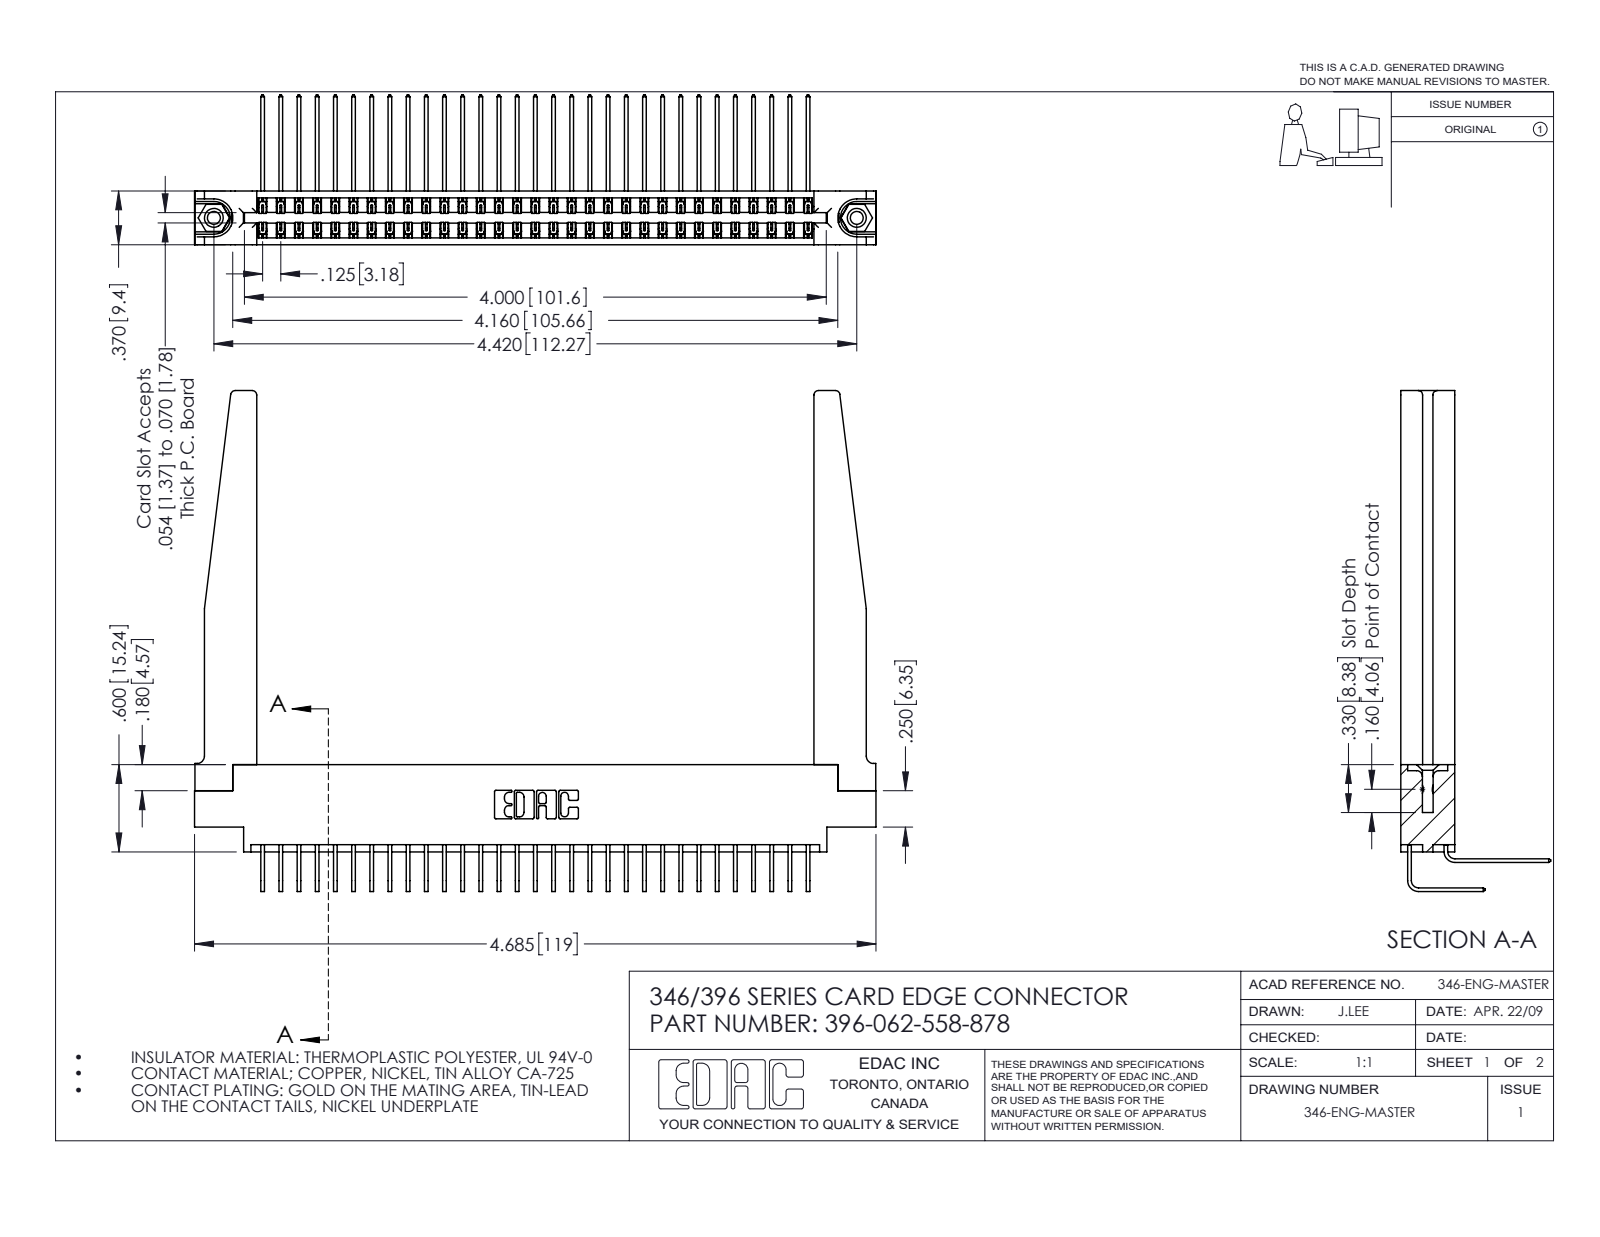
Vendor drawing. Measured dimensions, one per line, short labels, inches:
name: 346-220-078_345-220-078; 396-062-558-878; 346 Part_0.170 Offset - 0.156 Dia-TH; 345-292-001_558 Tail - 2 (+2 more)
written by: SolidWorks 2016 (CONFIG_CONTROL_DESIGN)
unit: in
bodies: 67 solids, 3708 faces (2516 planar, 1140 cylindrical, 52 other)
size: 4.685 × 3.443 × 1.03
volume: 1.137 in³; area: 37.78 in²
holes: 2× ⌀0.089, 2× ⌀0.125, 2× ⌀0.156, 1× ⌀0.064
bosses: 2× ⌀0.155
rounds: 93× R0.006, 22× R0.01, 8× R0.03, 6× R0.007, 6× R0.031, 4× R0.05, 3× R0.026, 2× R0.014
face distances: 0.37, 0.322, 0.048, 0.072, 0.025, 0.148, 0.15, 0.25, 0.298, 0.275
hole spacings: 0.246, 4.212, 4.42
